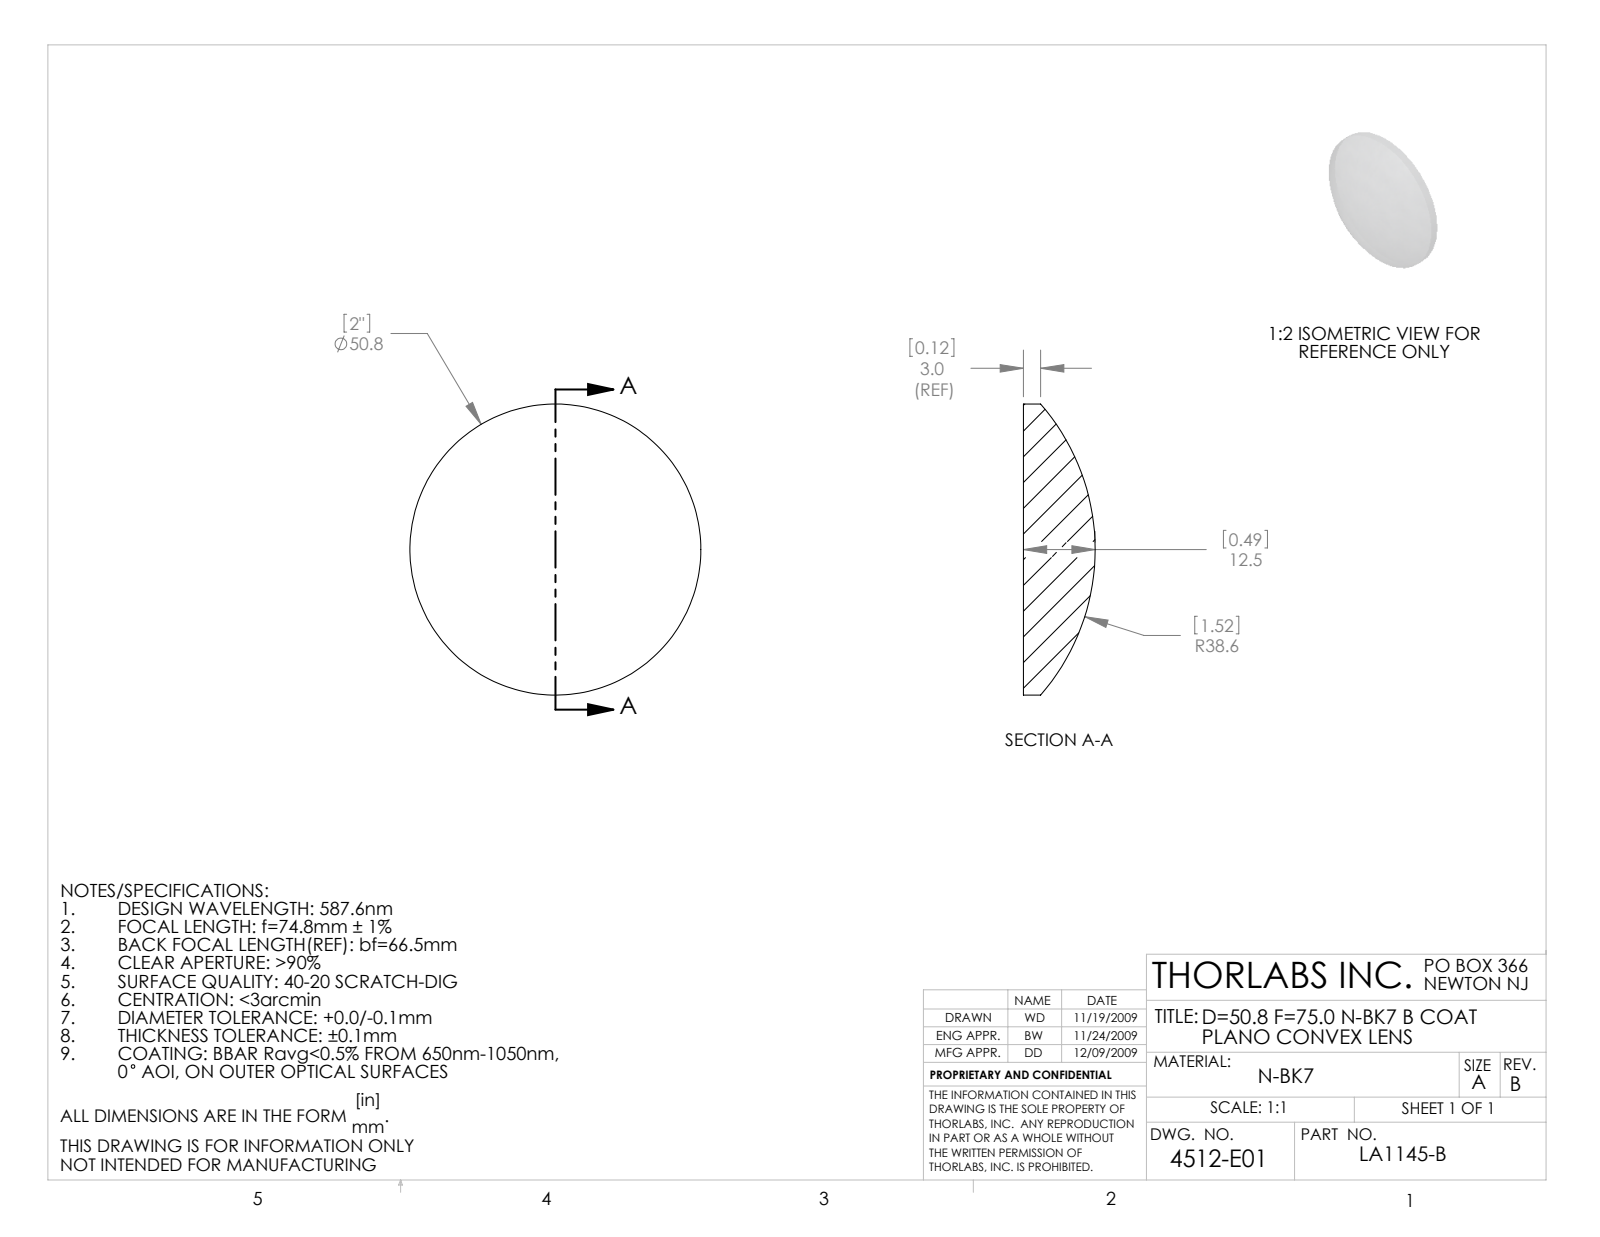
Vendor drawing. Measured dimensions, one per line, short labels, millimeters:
name: 4512-E0W
written by: SolidWorks 2009 (AUTOMOTIVE_DESIGN)
unit: mm
bodies: 1 solid, 5 faces (1 planar, 2 cylindrical, 2 other)
size: 50.8 × 50.8 × 12.52
volume: 16 176 mm³; area: 4 817 mm²
bosses: 1× ⌀50.8
